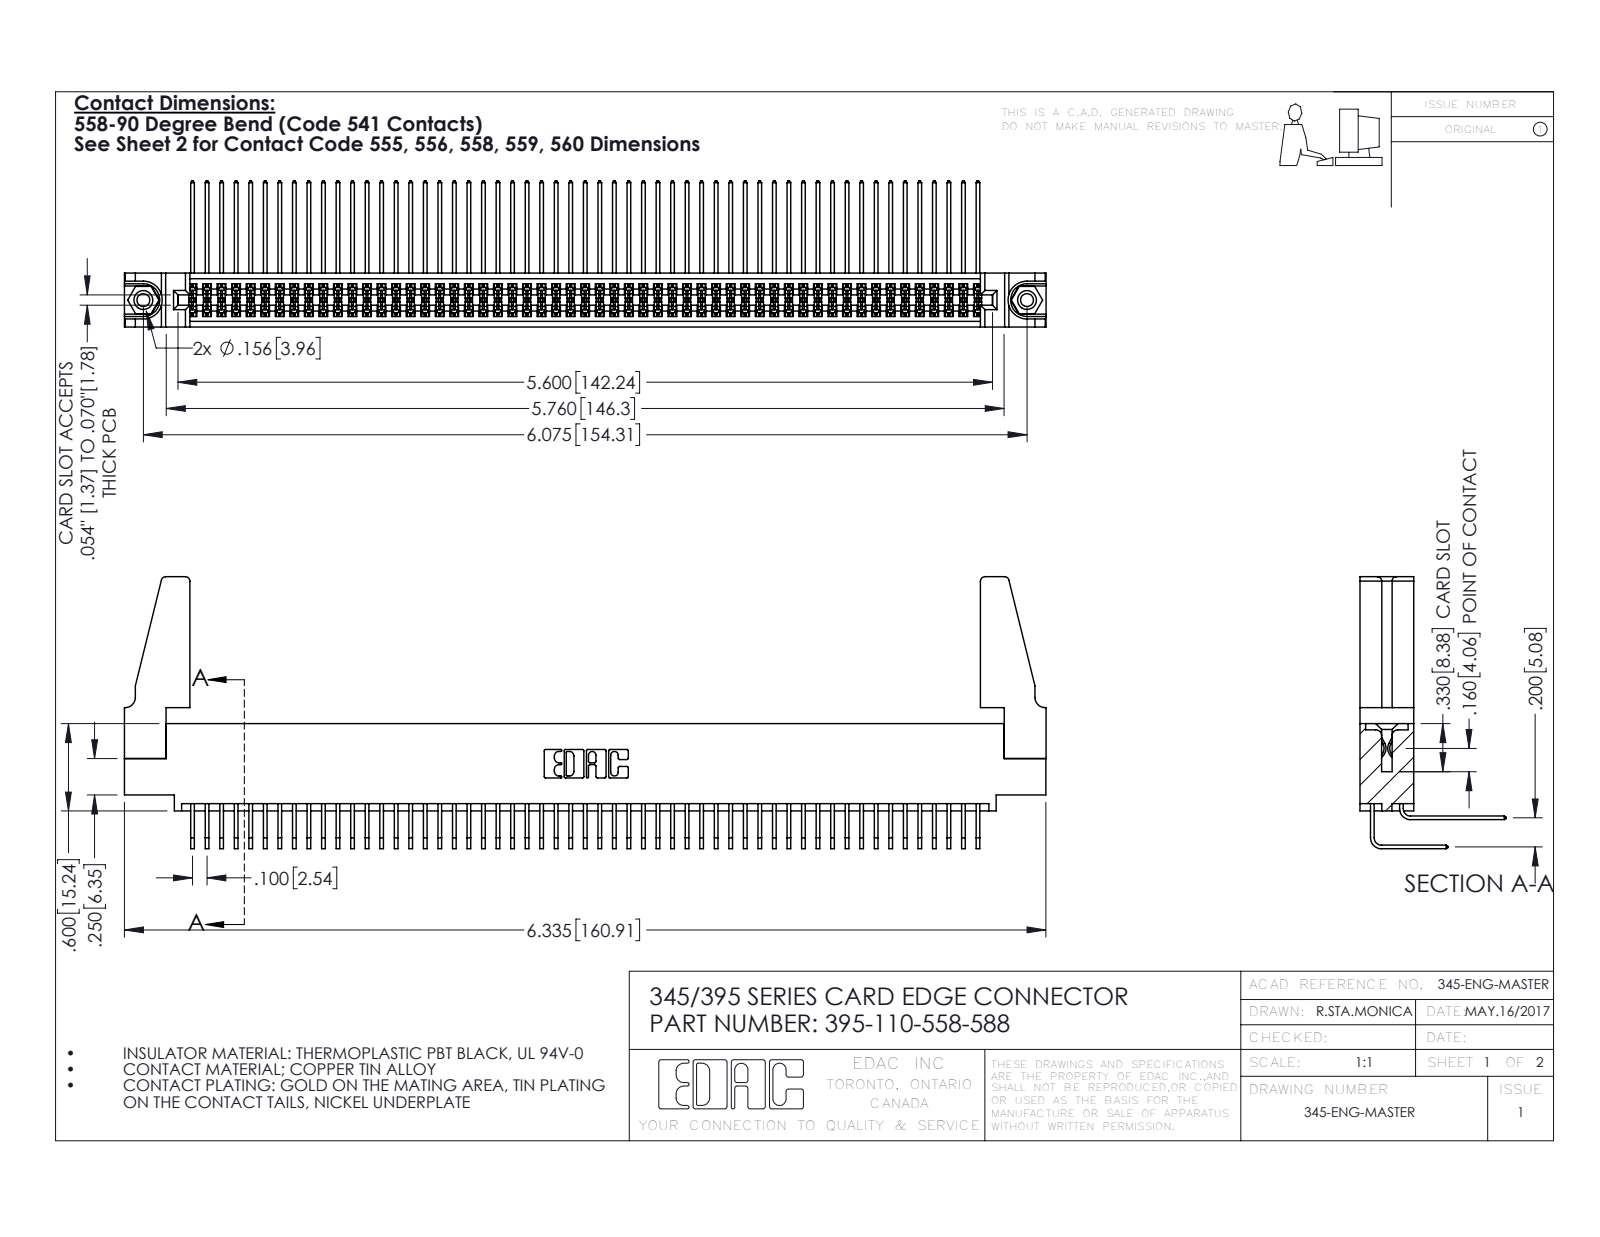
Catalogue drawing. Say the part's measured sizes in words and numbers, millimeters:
The part is named "345-220-078_345-220-088; 345-250-001_345-250-001-102; 345-292-001_558 Tail - 2; 345 Part_0.110 Offset - 0.156 Dia-TH (+2 more)". Its 3-D file was written by "SolidWorks 2016 (CONFIG_CONTROL_DESIGN)". It is 115 solids with 5974 faces: 4006 planar, 1952 cylindrical and 16 other. Overall it measures 160.9 by 47.5 by 25.5 millimeters. Its volume is 19 570 cubic millimeters and its surface area 30 570 square millimeters. Round holes: 2 of diameter 2.3, 2 of diameter 3.2, 2 of diameter 4, 1 of diameter 1.6. Round bosses or shafts: 2 of diameter 3.9. Partial cylindrical surfaces (rounded edges, fillets, slot ends): 165 of radius 0.2, 22 of radius 0.3, 8 of radius 0.8, 6 of radius 0.2, 6 of radius 0.8, 3 of radius 0.7, 2 of radius 0.4, 2 of radius 0.5. The main face-to-face distances are 1.8, 7.6, 5.1, 9.4, 2.5, 6.9, 0.6, 5.7, 0.6, 4.4. The hole center spacings are 6.9, 148.3, 154.3.
